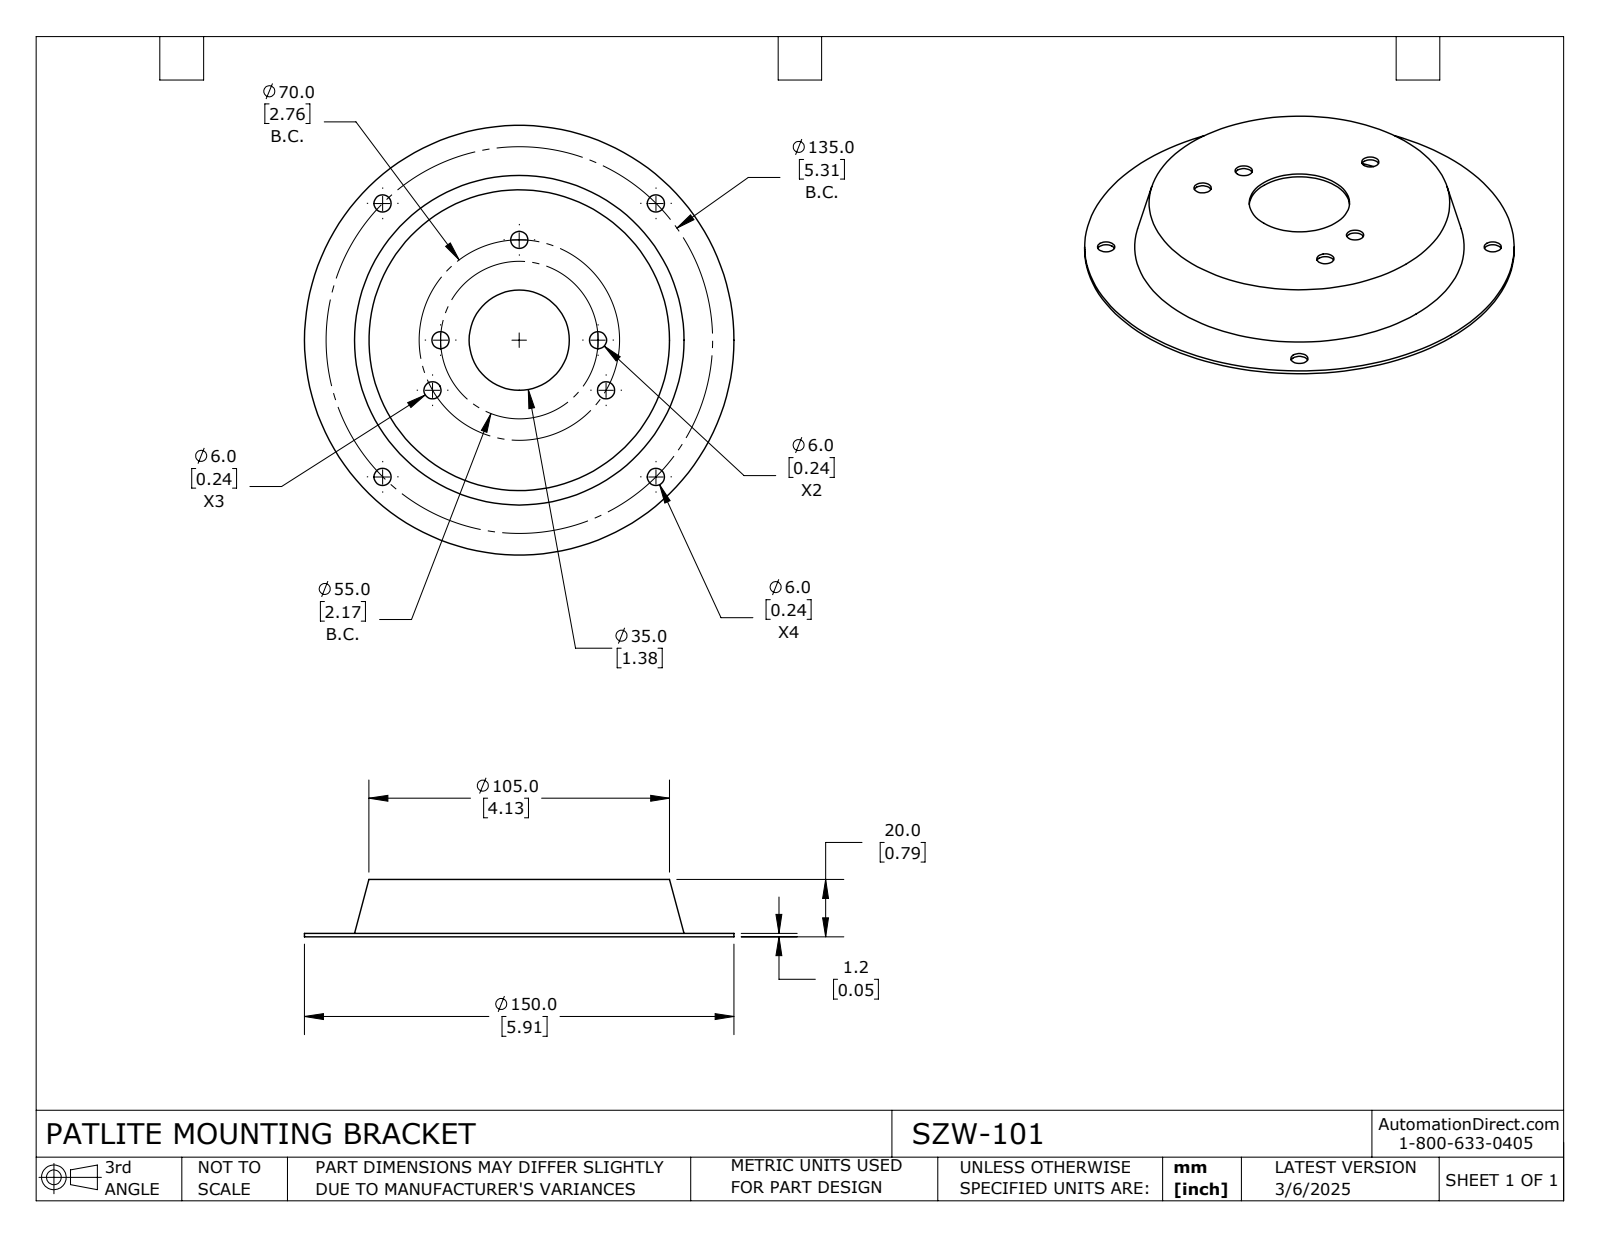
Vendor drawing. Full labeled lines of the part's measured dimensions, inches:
Part name (STEP PRODUCT): SZW-101
STEP written by: SolidWorks 2024 (CONFIG_CONTROL_DESIGN)
Units: inches
Bodies: 1 solid, 30 faces (4 planar, 22 cylindrical, 4 other)
Overall size (bounding box): 5.906 × 5.906 × 0.787
Volume: 1.567 in³ · Surface area: 67.74 in²
Round holes (diameter × count): ⌀0.236 ×9, ⌀1.378 ×1
Round bosses / shafts (diameter × count): ⌀5.906 ×1
Main face-to-face distances: 0.047, 0.74, 0.787, 0.693
Hole centre spacings: 2.041, 2.657, 3.507, 3.758, 1.378, 2.387, 0.698, 1.083
